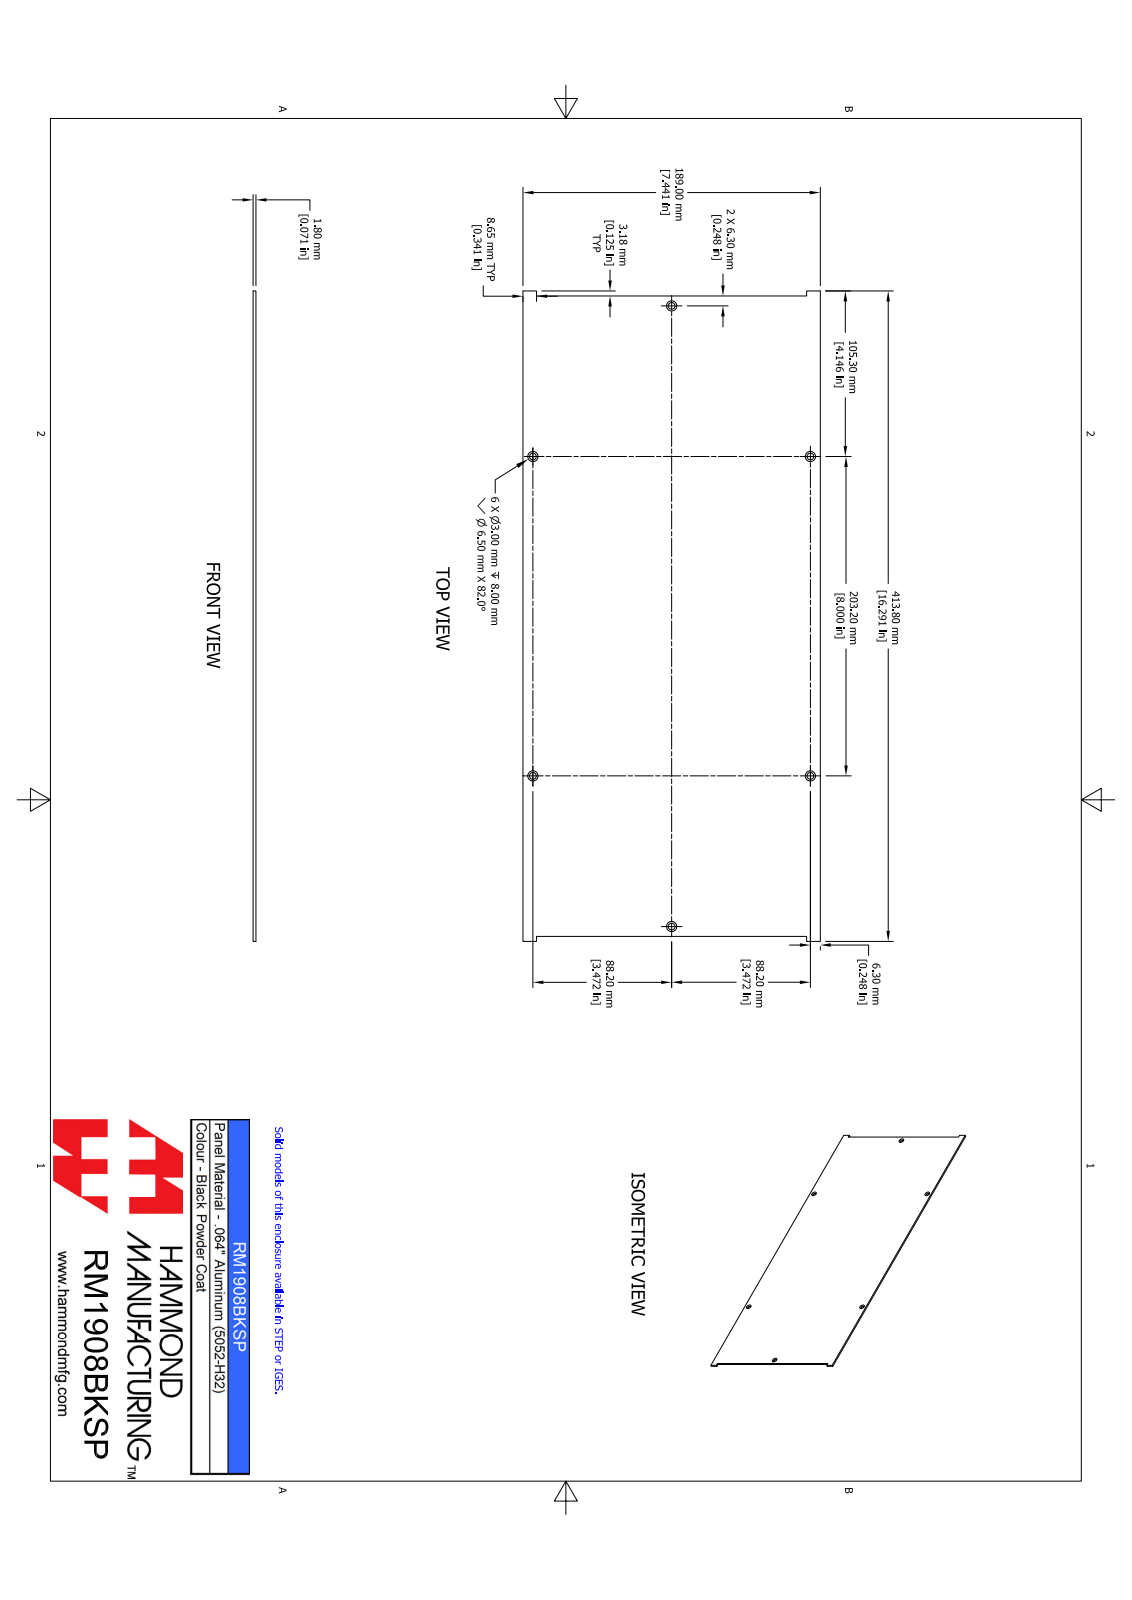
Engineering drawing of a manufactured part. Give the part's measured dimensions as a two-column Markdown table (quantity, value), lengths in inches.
| quantity | value |
| --- | --- |
| part name | RM1908BKSP |
| STEP written by | SolidWorks 2021 (AUTOMOTIVE_DESIGN) |
| units | inches |
| bodies | 1 solid, 26 faces (14 planar, 6 cylindrical, 6 other) |
| overall size | 16.291 × 7.441 × 0.071 |
| volume | 8.457 in³ |
| surface area | 242.4 in² |
| round holes (diameter × count) | 0.169 × 6 |
| main face-to-face distances | 0.071, 7.441, 16.041, 16.166, 0.125, 0.125, 16.167, 16.291, 0.341, 7.1 |
| hole center spacings | 5.127, 12.274, 6.945, 8, 10.594, 15.545 |
